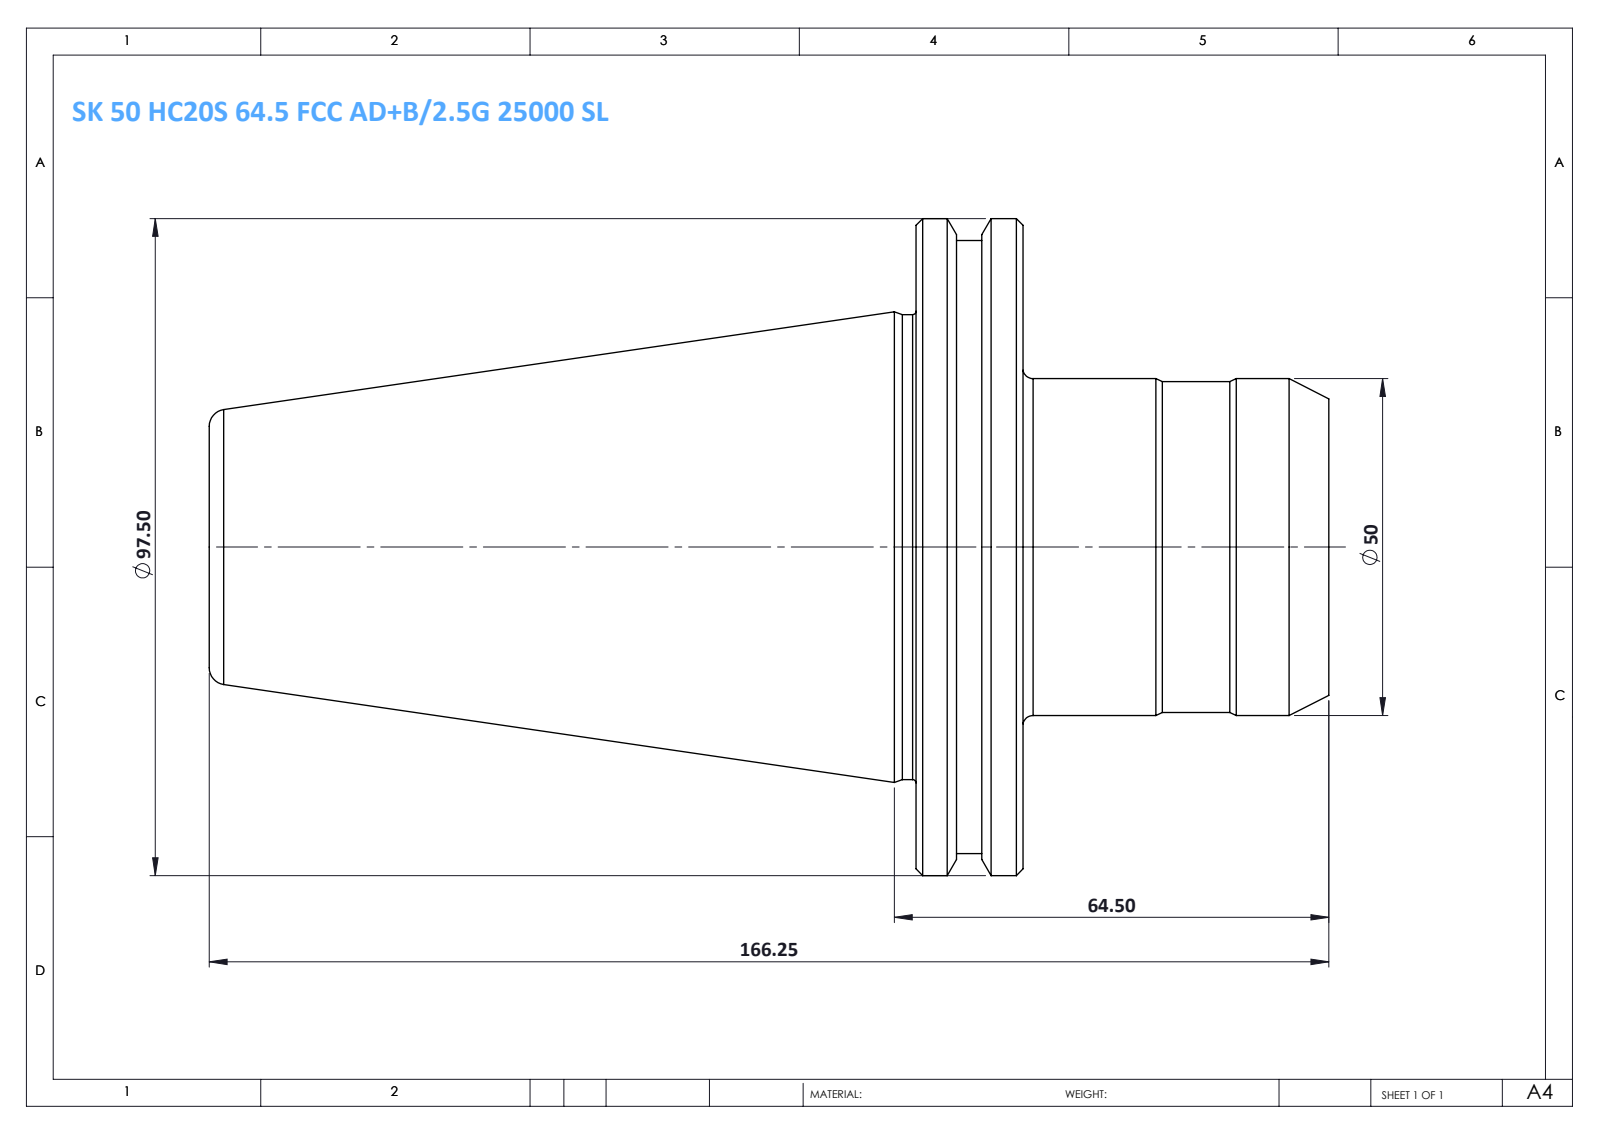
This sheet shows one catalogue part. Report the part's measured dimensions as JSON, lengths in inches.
{"part_name": "SK 50 HC20S 64.5 FCC AD+B -2.5G 25000 SL", "step_written_by": "SolidWorks 2014 (CONFIG_CONTROL_DESIGN)", "units": "inches", "bodies": {"solids": 1, "faces": 46, "planar": 6, "cylindrical": 14, "other": 26}, "overall_size": [6.545, 3.839, 3.839], "volume_in3": 28.1, "surface_area_in2": 66.92, "round_bosses_or_shafts": [[3.839, 1], [3.583, 1], [2.717, 1], [1.969, 1], [1.933, 1]], "face_to_face_distances": [0.626, 1.787, 2.413, 6.545, 4.758, 4.132, 2.028, 0.241, 0.385, 4.517]}
